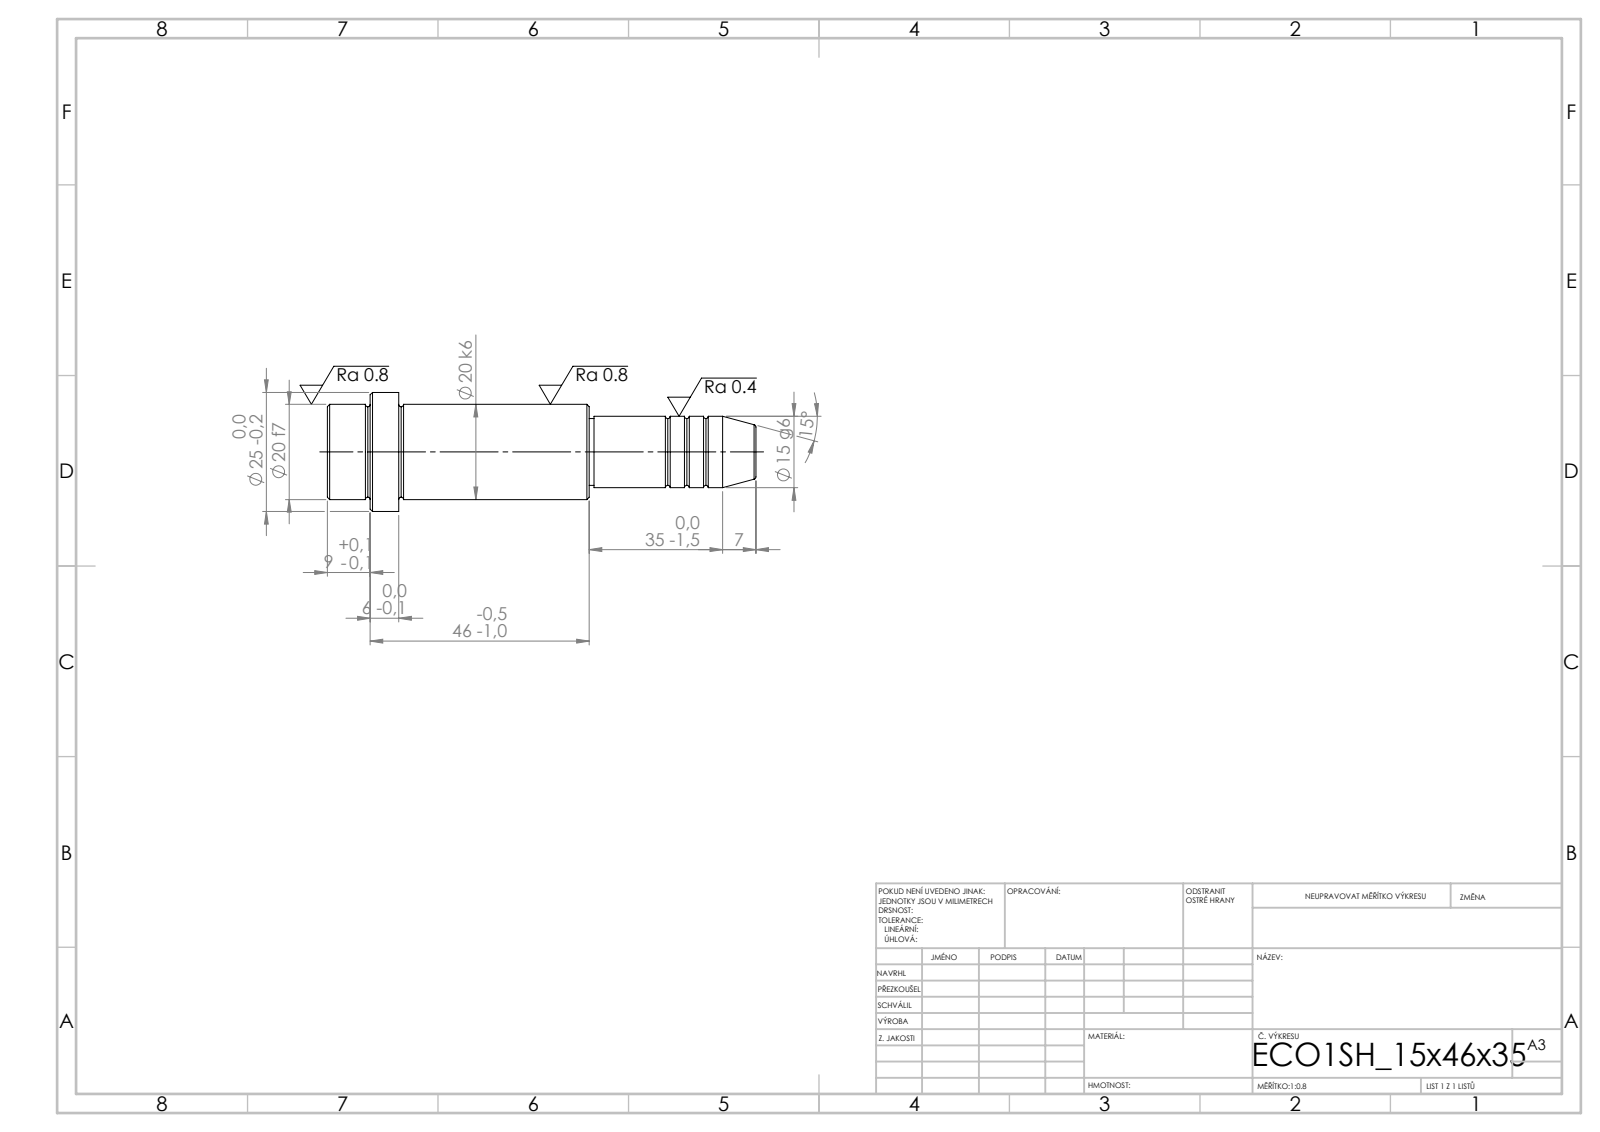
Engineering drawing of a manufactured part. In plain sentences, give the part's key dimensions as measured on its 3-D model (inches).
Its 3-D file was written by "SolidWorks 2019 (CONFIG_CONTROL_DESIGN)". It is 1 solid with 52 faces: 6 planar, 16 cylindrical and 30 other. Overall it measures 3.543 by 0.984 by 0.984 inches. Its volume is 1.47 cubic inches and its surface area 9.59 square inches. Round bosses or shafts: 1 of diameter 0.984, 1 of diameter 0.787, 1 of diameter 0.591, 1 of diameter 0.551. The main face-to-face distances are 0.591, 0.236, 0.354, 1.575, 1.811, 2.165, 1.378, 2.953, 3.189, 3.543.
